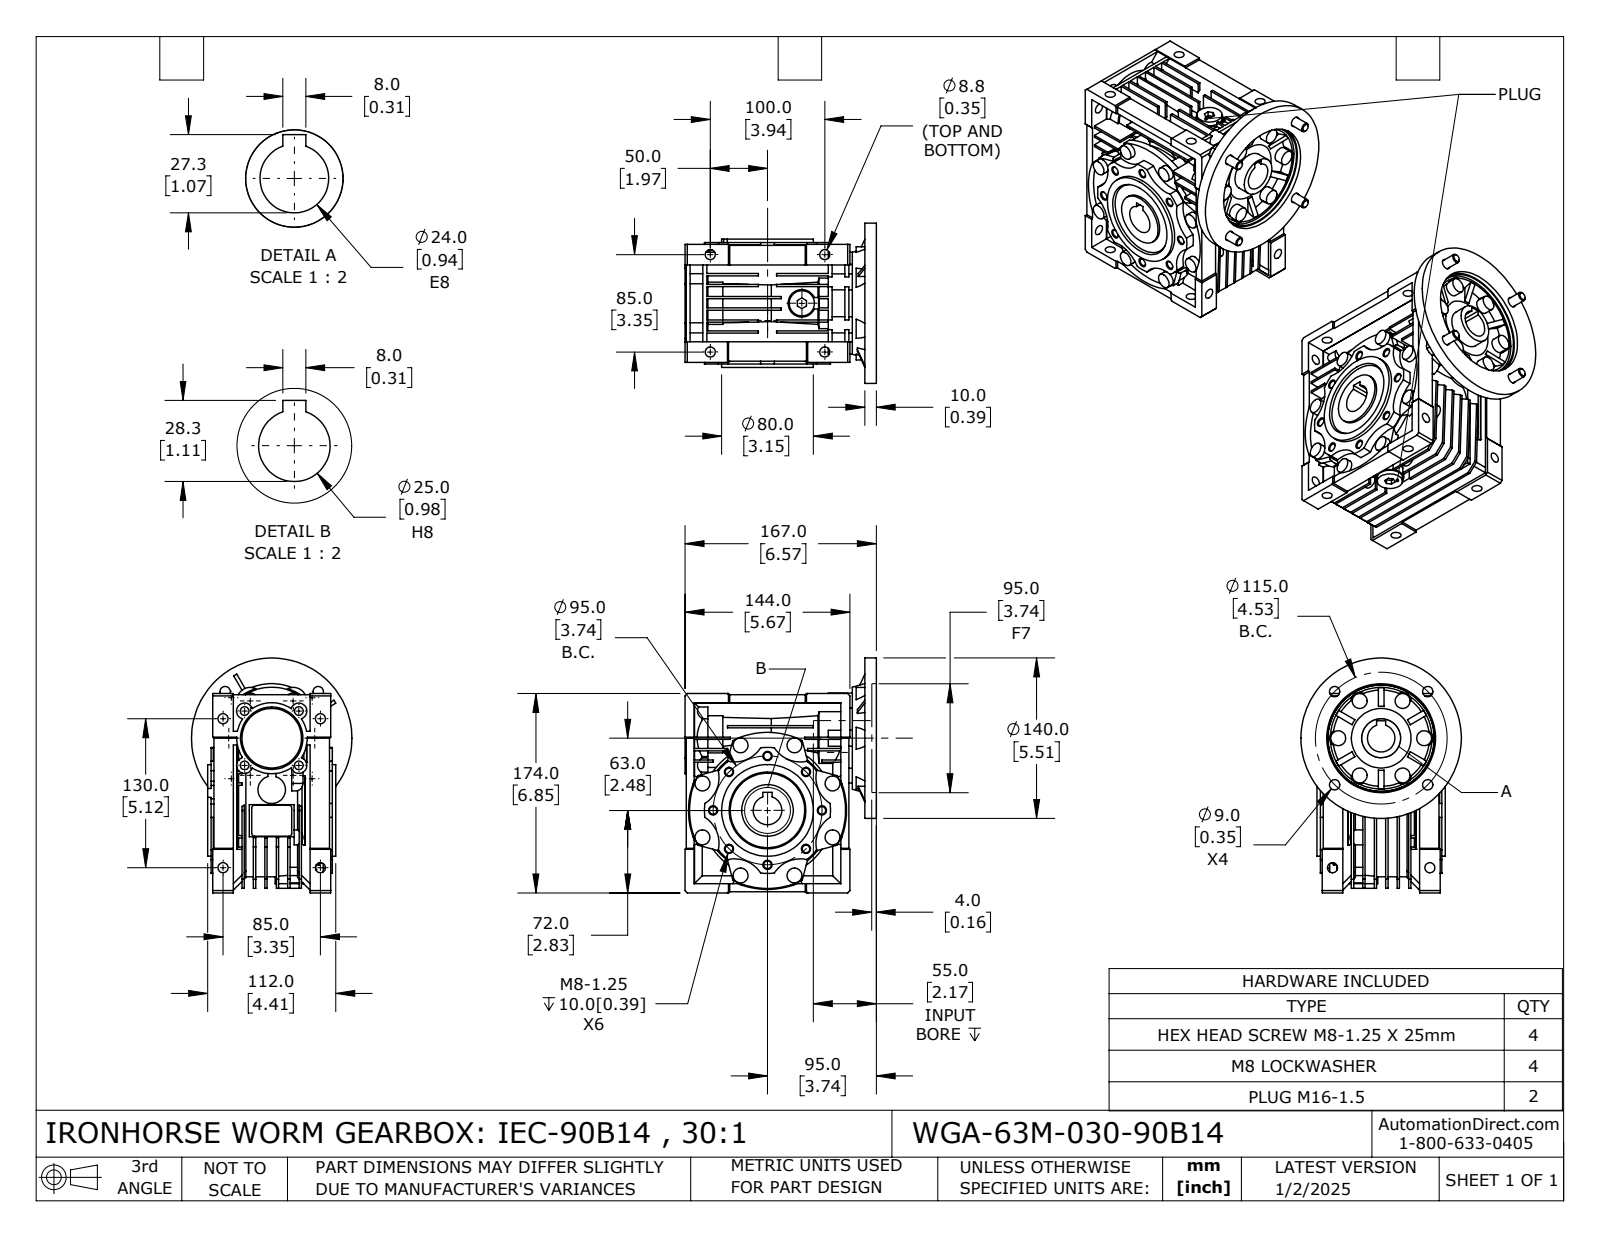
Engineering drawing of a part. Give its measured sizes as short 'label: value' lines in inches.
name: WGA-63M-030-90B14
written by: SolidWorks 2024 (CONFIG_CONTROL_DESIGN)
unit: in
bodies: 16 solids, 1375 faces (833 planar, 365 cylindrical, 177 other)
size: 8.071 × 7.087 × 5.512
volume: 114.1 in³; area: 561.5 in²
holes: 8× ⌀0.262, 8× ⌀0.346, 4× ⌀0.298, 4× ⌀0.323, 4× ⌀0.354, 2× ⌀0.571, 2× ⌀0.984, 1× ⌀0.945, 1× ⌀1.339, 1× ⌀1.457, 1× ⌀1.772, 1× ⌀2.047
bosses: 14× ⌀0.512, 4× ⌀0.606, 4× ⌀0.315, 3× ⌀0.945, 2× ⌀0.866, 2× ⌀0.622, 2× ⌀0.539, 1× ⌀5.512
rounds: 10× R0.276, 8× R1.063, 6× R0.295, 6× R0.469, 4× R0.098, 1× R0.329, 1× R1.161, 1× R1.201
face distances: 0.394, 0.315, 0.787, 0.079, 1.181, 0.472, 0.276, 0.709, 1.575, 0.827
hole spacings: 1.431, 1.87, 2.62, 2.645, 3.456, 0.945, 1.319, 1.865
